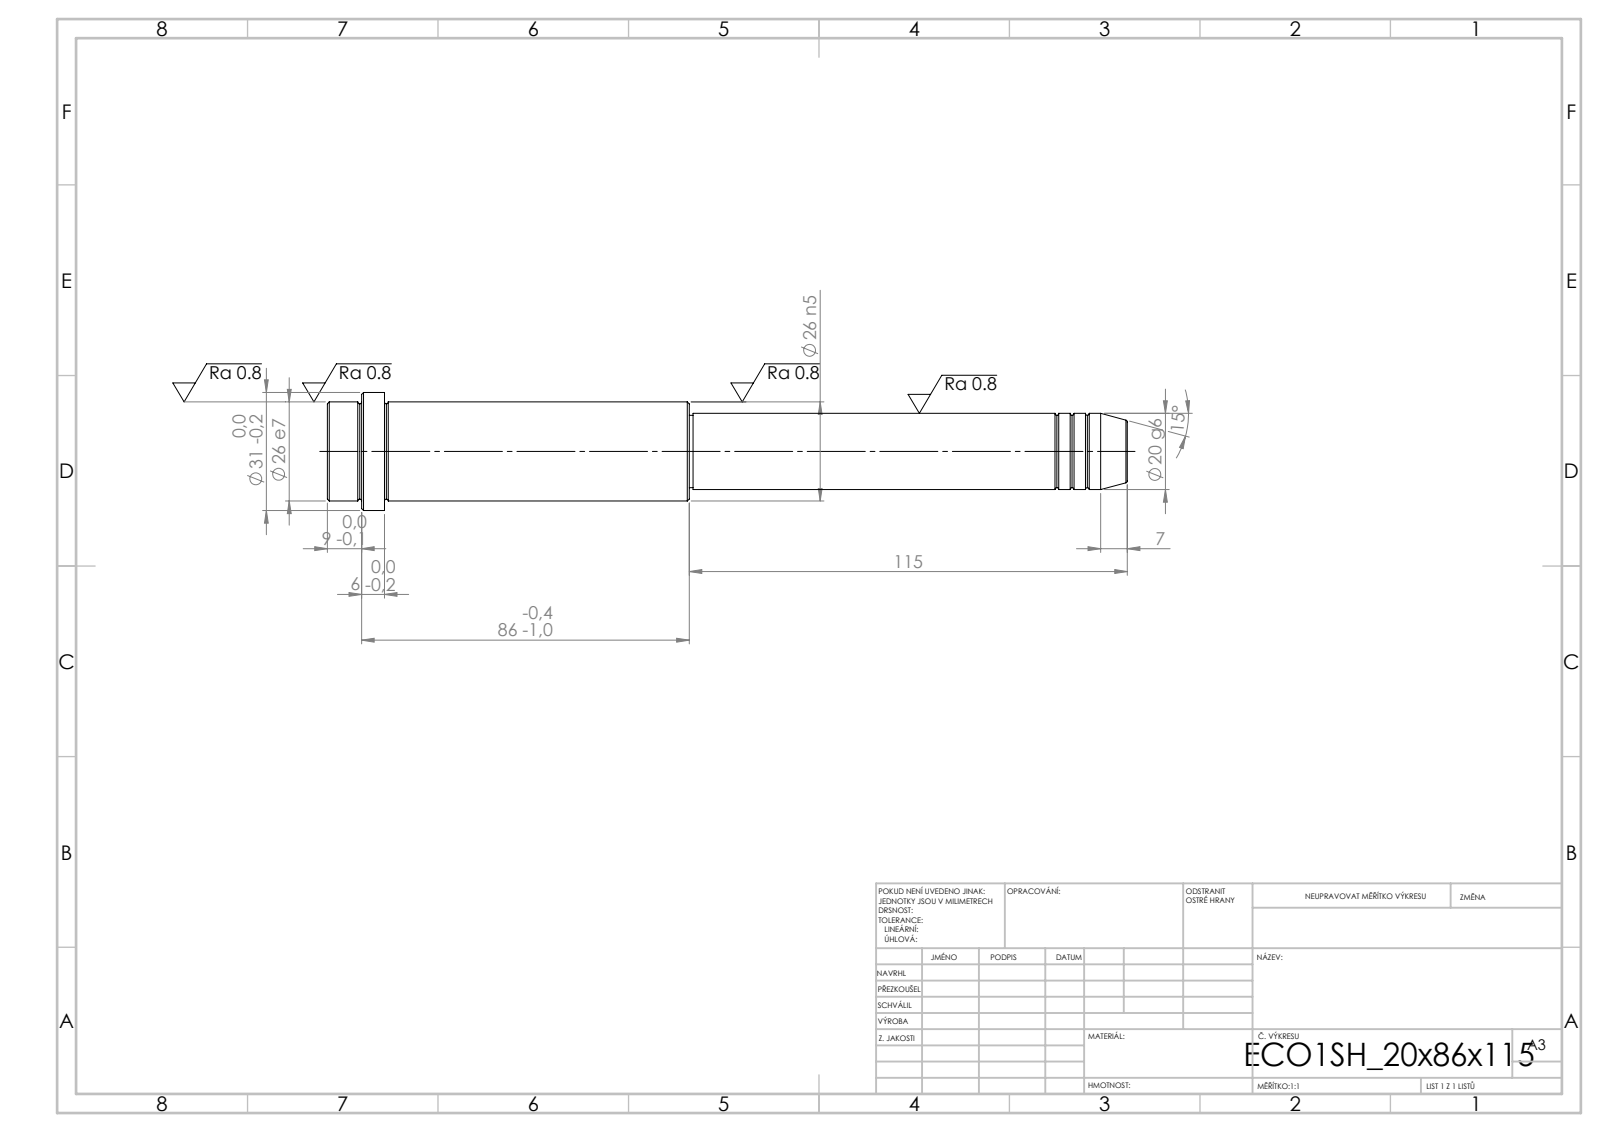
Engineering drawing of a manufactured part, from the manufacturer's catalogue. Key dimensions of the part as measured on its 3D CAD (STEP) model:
STEP written by: SolidWorks 2019 (CONFIG_CONTROL_DESIGN)
Units: millimetres
Bodies: 1 solid, 52 faces (6 planar, 16 cylindrical, 30 other)
Overall size (bounding box): 210 × 31 × 31
Volume: 87 323 mm³ · Surface area: 16 615 mm²
Round bosses / shafts (diameter × count): ⌀31 ×1, ⌀26 ×1, ⌀20 ×1, ⌀19 ×1
Main face-to-face distances: 15, 80, 95, 115, 195, 210, 201, 86, 6, 9
